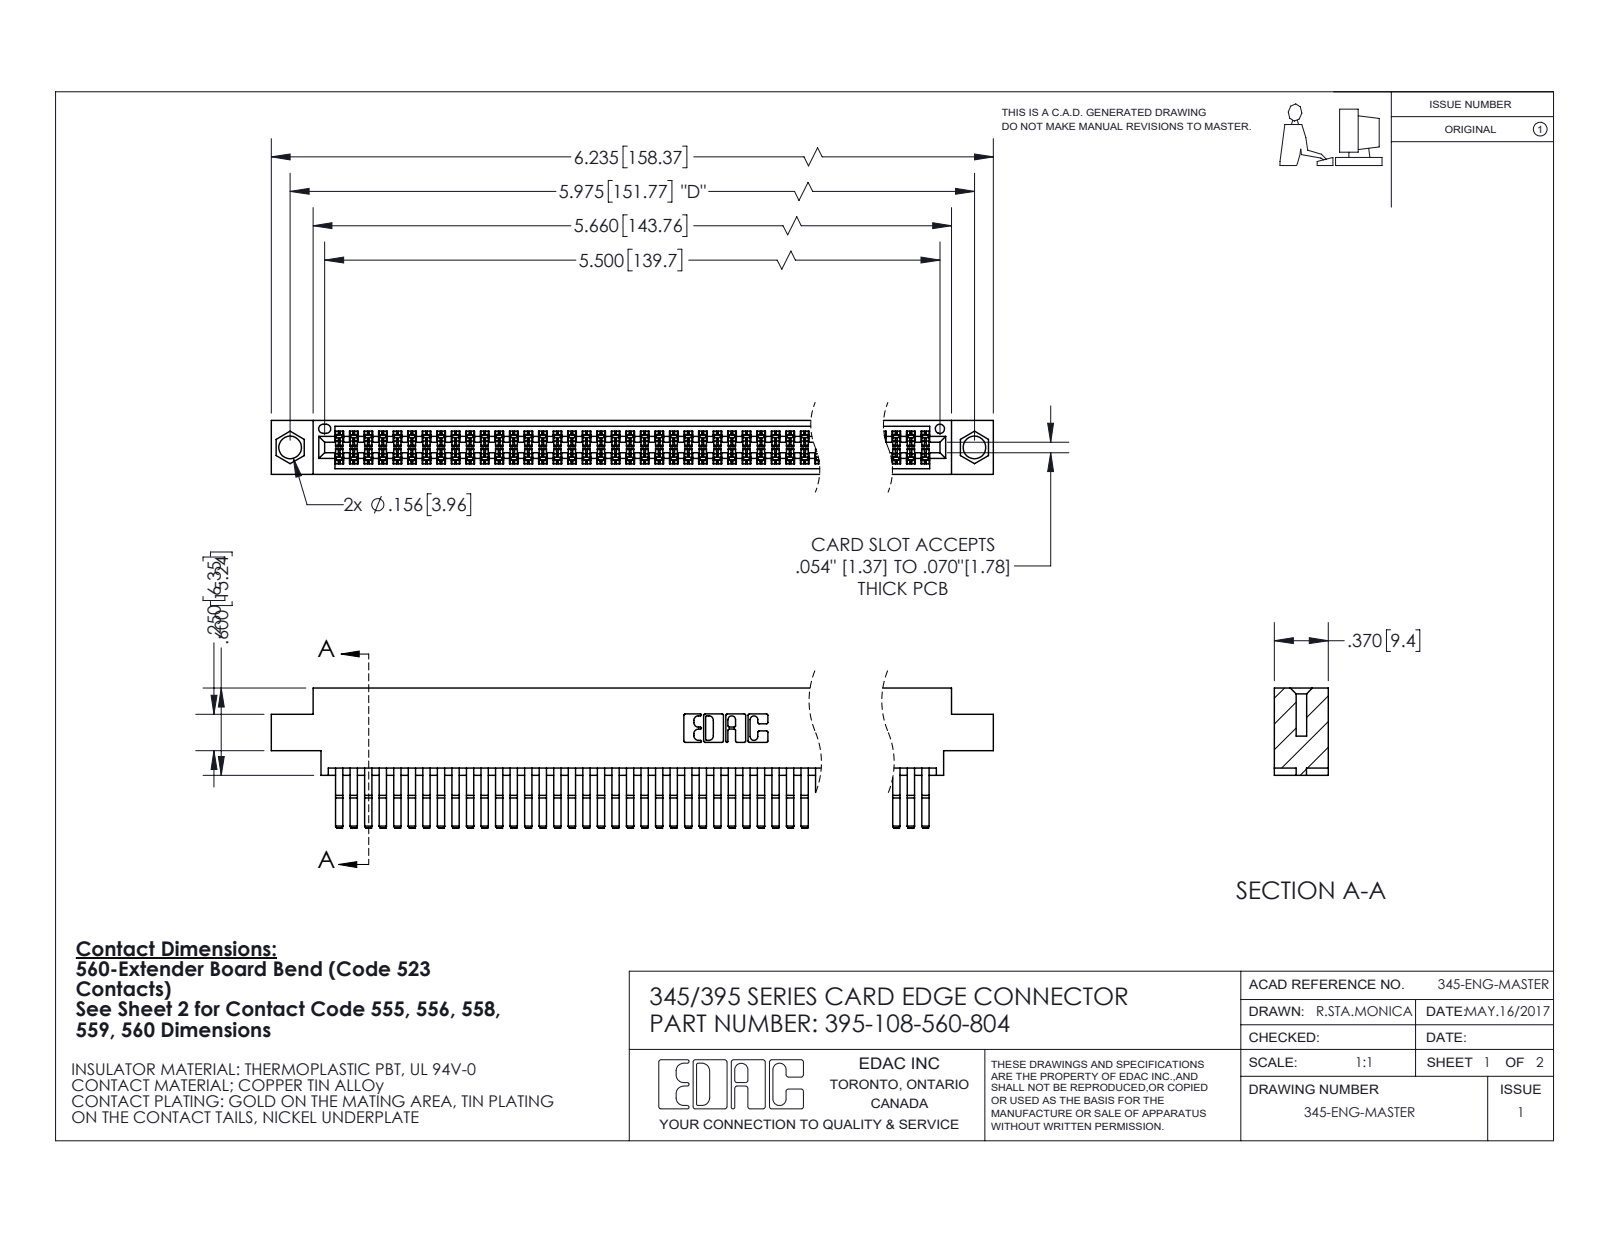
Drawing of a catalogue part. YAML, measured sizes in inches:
part_name: "345-292-001_560 Tail; 345 Part_0.170 Offset - 0.156 Dia-TI; 395-108-560-804"
step_written_by: "SolidWorks 2020 (CONFIG_CONTROL_DESIGN)"
units: inches
bodies: {solids: 109, faces: 5760, planar: 3662, cylindrical: 2098, other: 0}
overall_size: [6.235, 0.962, 0.37]
volume: 0.975
surface_area: 39.8
round_holes:
  - {diameter: 0.156, count: 2}
  - {diameter: 0.064, count: 1}
partial_cylinders:
  - {radius: 0.006, count: 216}
  - {radius: 0.01, count: 22}
  - {radius: 0.007, count: 6}
  - {radius: 0.031, count: 6}
  - {radius: 0.026, count: 3}
  - {radius: 0.01, count: 2}
  - {radius: 0.014, count: 2}
  - {radius: 0.019, count: 2}
face_to_face_distances: [0.025, 0.072, 0.298, 0.37, 0.2, 0.098, 0.272, 0.225, 0.175, 0.149]
hole_center_spacings: [0.27, 5.739, 5.975]
